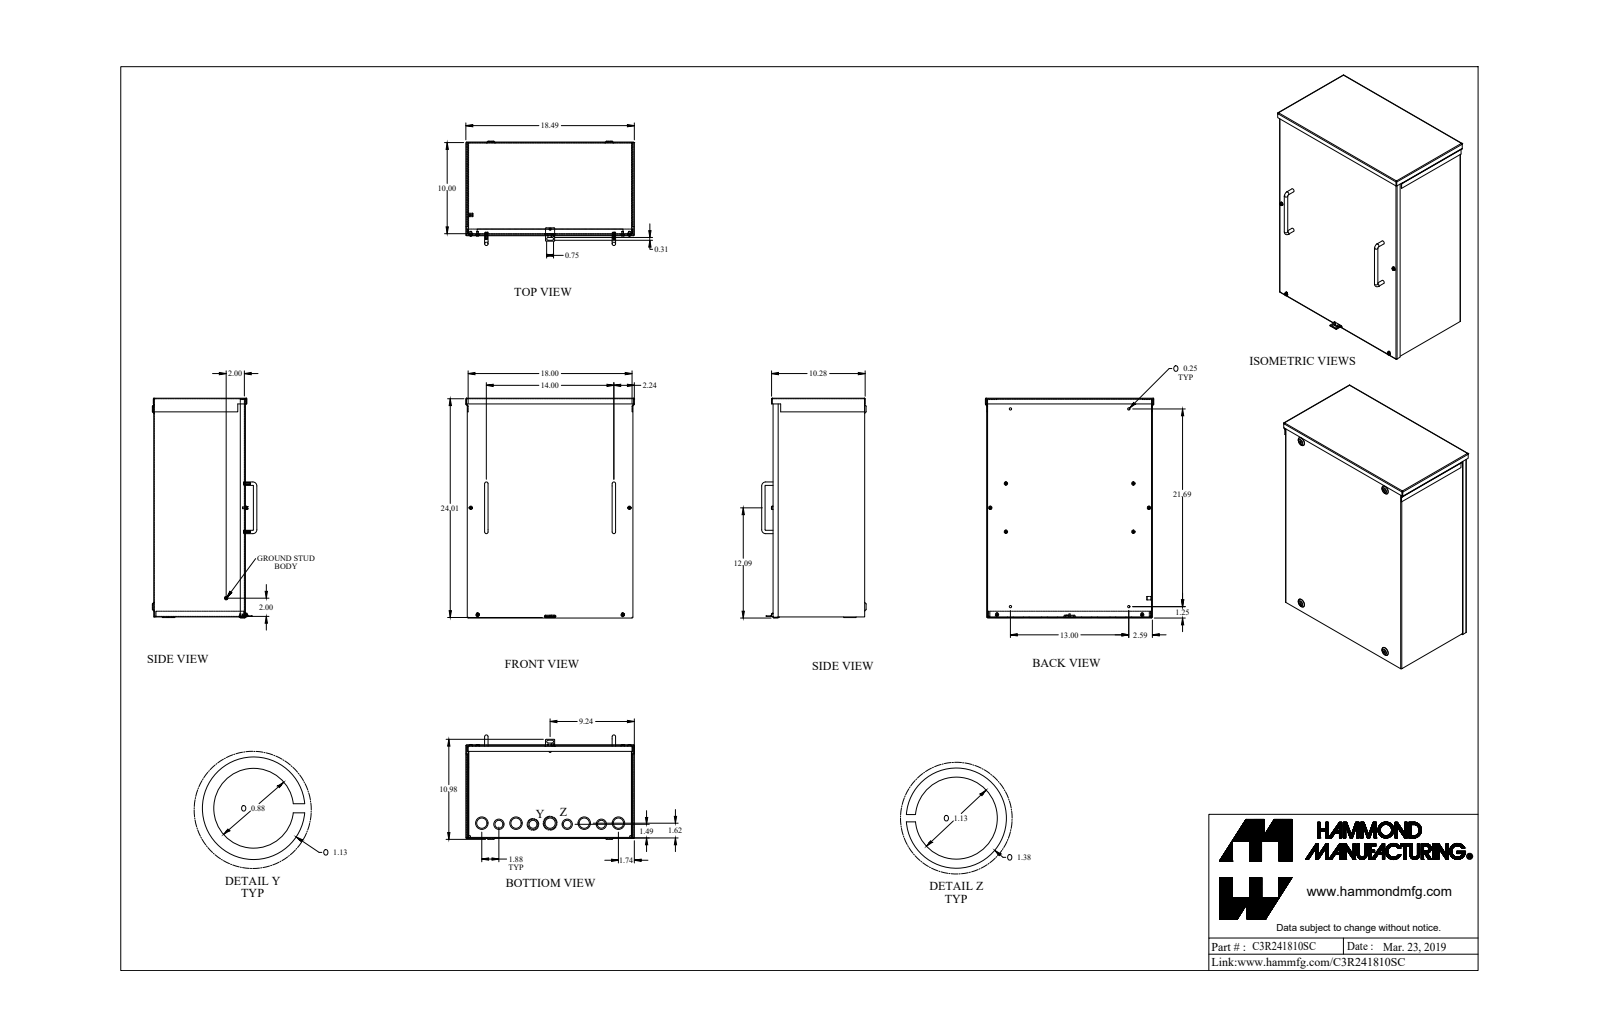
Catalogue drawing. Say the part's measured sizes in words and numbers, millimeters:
The part is named "C3R241810SC_Default". Its 3-D file was written by "SolidWorks 2019 (CONFIG_CONTROL_DESIGN)". It is 17 solids with 609 faces: 314 planar, 177 cylindrical and 118 other. Overall it measures 612.6 by 469.6 by 291.2 millimeters. Its volume is 1 758 000 cubic millimeters and its surface area 2 414 000 square millimeters. Round holes: 5 of diameter 4, 4 of diameter 4.3, 4 of diameter 5.2, 4 of diameter 6.4, 3 of diameter 28.6, 2 of diameter 22.2, 2 of diameter 22.2, 2 of diameter 28.6, 1 of diameter 3.2, 1 of diameter 3.5. Round bosses or shafts: 9 of diameter 9.5, 8 of diameter 4.8, 4 of diameter 28.6, 4 of diameter 9.3, 3 of diameter 34.9, 2 of diameter 34.9, 2 of diameter 9.5, 1 of diameter 3.2. Partial cylindrical surfaces (rounded edges, fillets, slot ends): 21 of radius 0.7, 21 of radius 2.2, 8 of radius 2.8, 8 of radius 3.2, 2 of radius 4. The main face-to-face distances are 1.4, 254, 455.8, 252.6, 255.4, 457.2, 454.3, 1.4, 606.7, 608.2. The hole center spacings are 355.6, 95.3, 0.5, 47.7, 47.8, 80.1, 134.6, 142.9.
